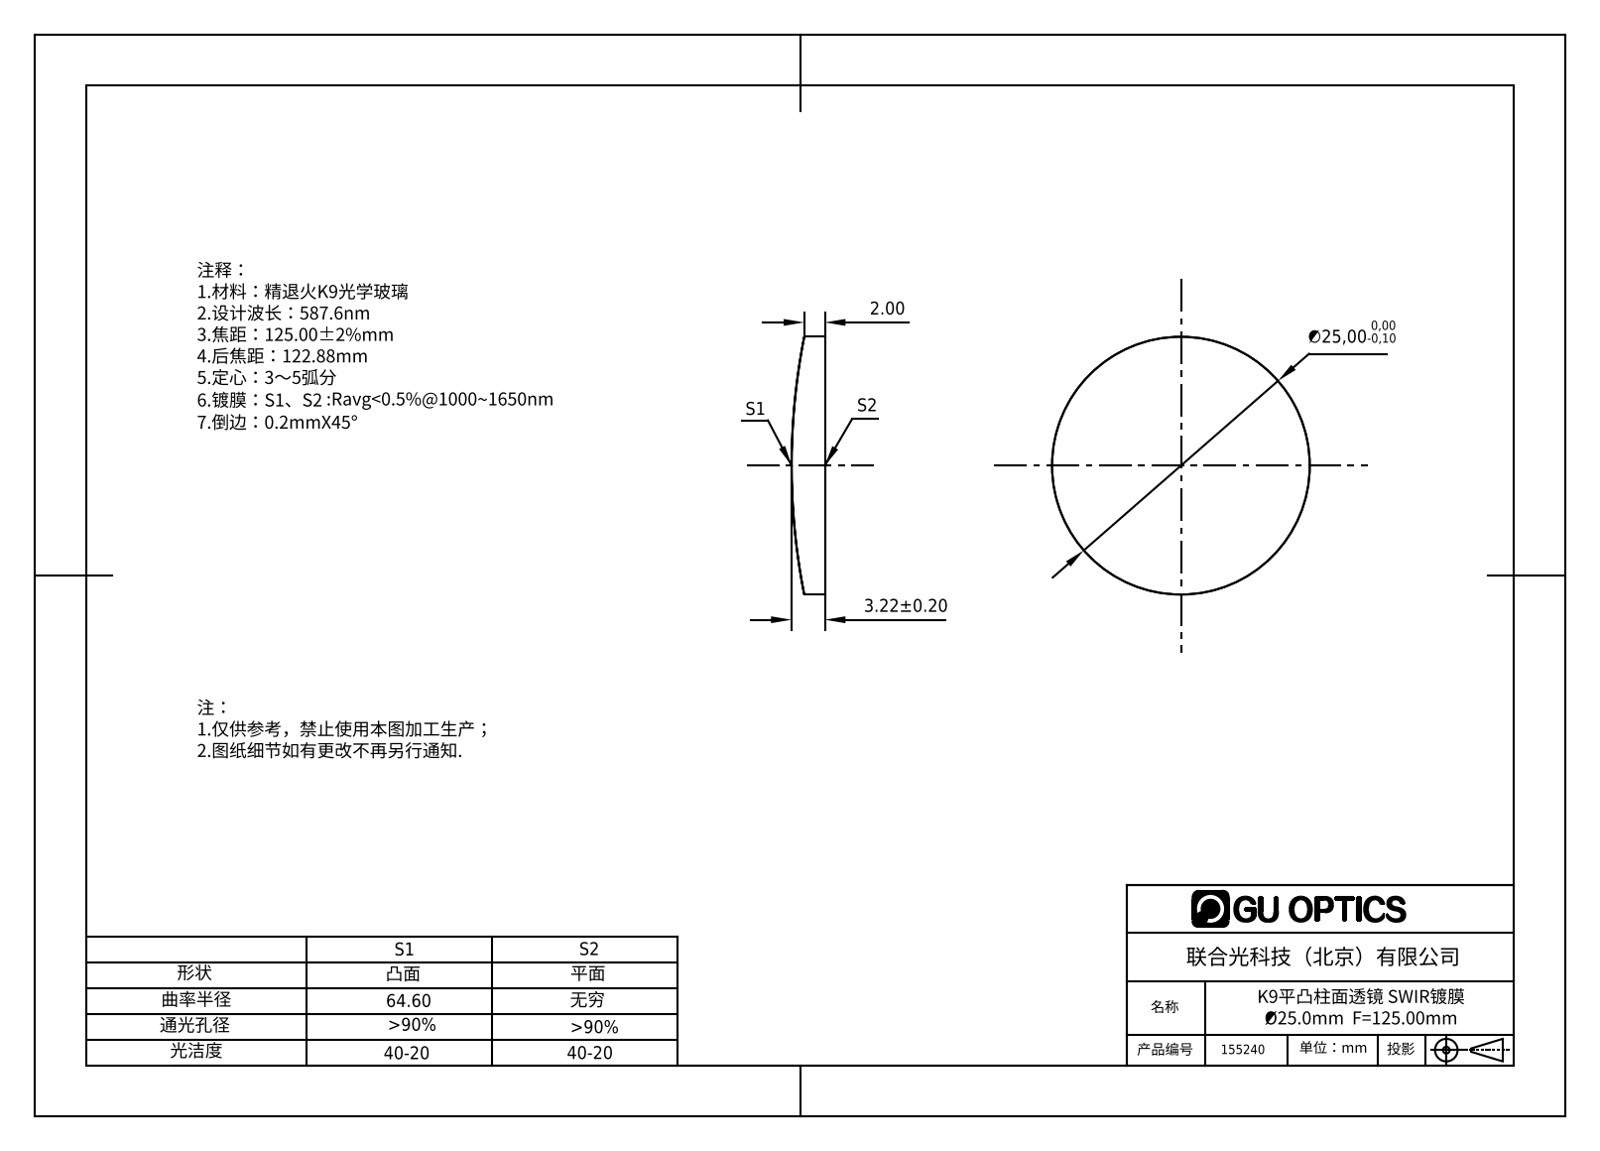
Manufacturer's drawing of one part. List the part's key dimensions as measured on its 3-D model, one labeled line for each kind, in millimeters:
Part name (STEP PRODUCT): 155042
STEP written by: SolidWorks 2016 (AUTOMOTIVE_DESIGN)
Units: millimetres
Bodies: 1 solid, 4 faces (1 planar, 3 cylindrical, 0 other)
Overall size (bounding box): 25 × 25 × 3.22
Volume: 1 432 mm³ · Surface area: 1 189 mm²
Round bosses / shafts (diameter × count): ⌀25 ×1
Partial cylindrical surfaces — rounded edges, fillets, slot ends (radius × count): R64.6 ×1
